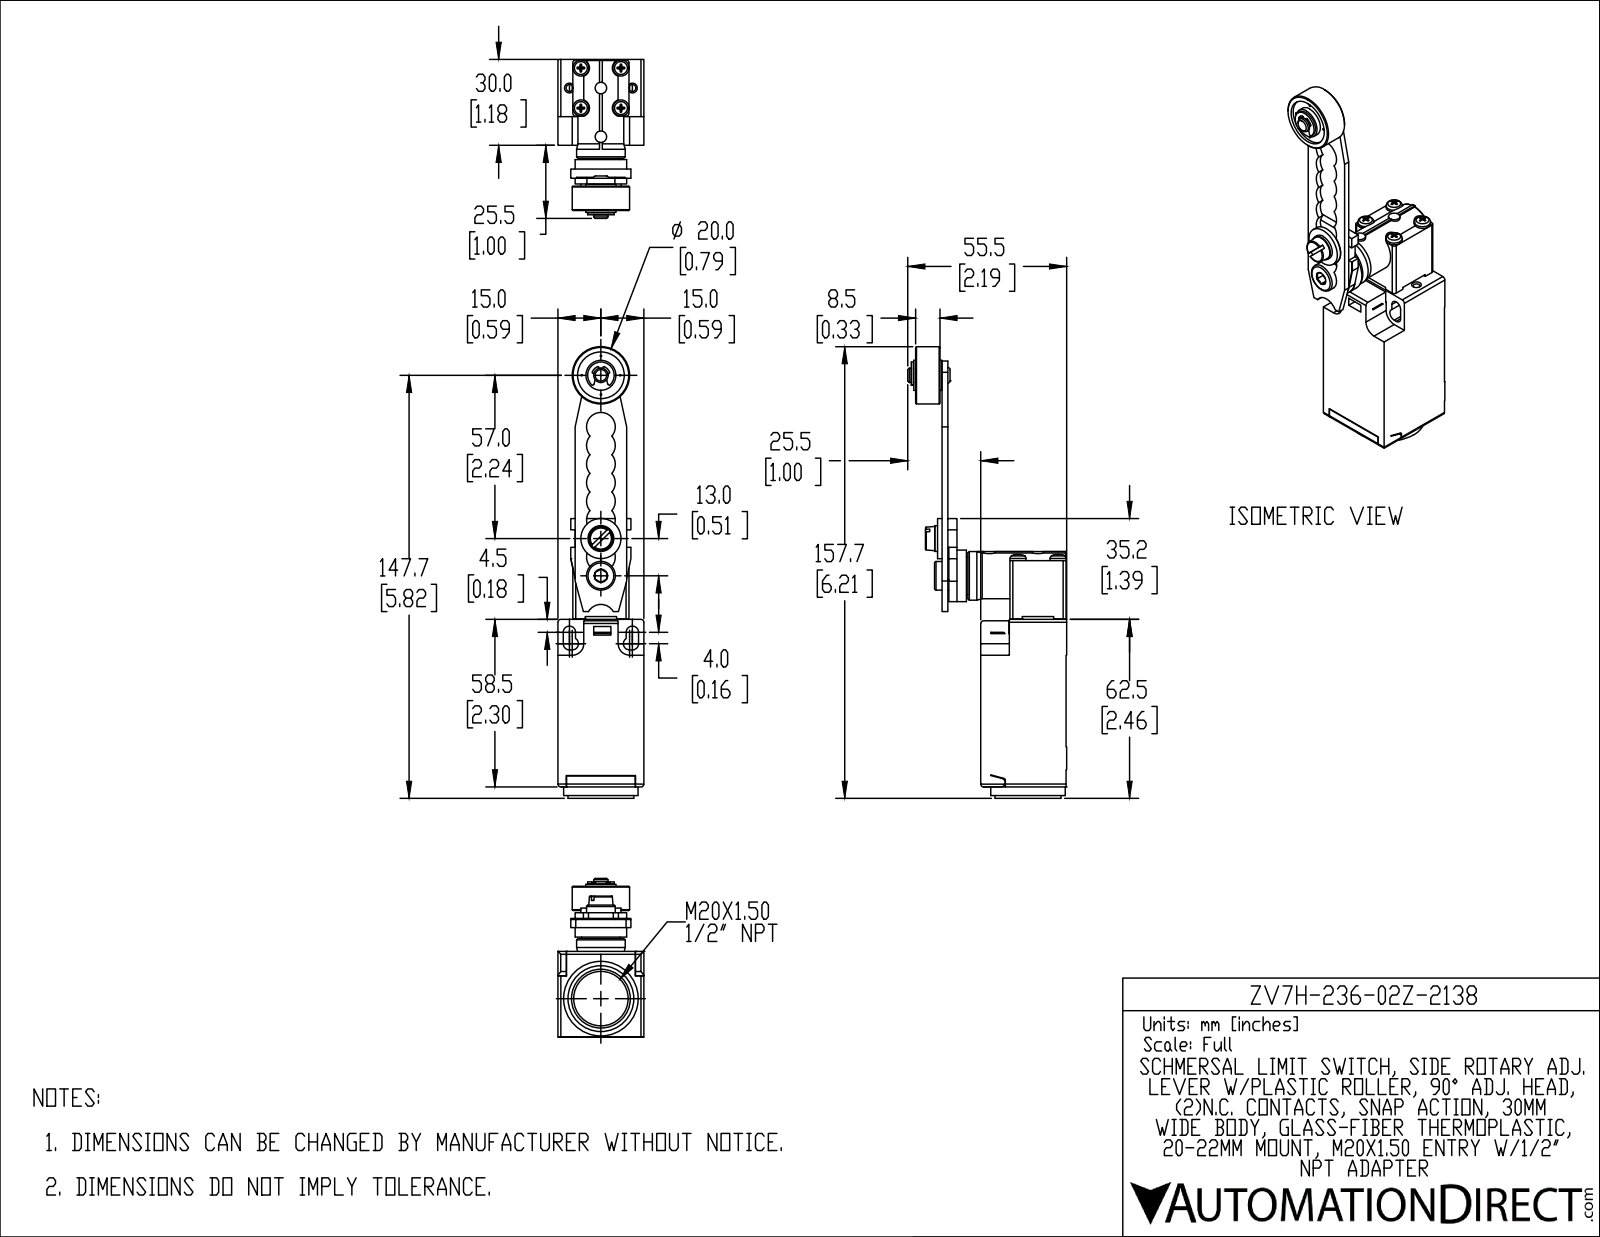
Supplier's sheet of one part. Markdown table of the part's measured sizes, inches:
| quantity | value |
| --- | --- |
| part name | ZV7H-236-02Z-2138 |
| STEP written by | SolidWorks 2019 (CONFIG_CONTROL_DESIGN) |
| units | inches |
| bodies | 6 solids, 542 faces (303 planar, 184 cylindrical, 55 other) |
| overall size | 6.209 × 2.185 × 1.181 |
| volume | 4.049 in³ |
| surface area | 32.22 in² |
| round holes (diameter × count) | 0.094 × 6, 0.02 × 4, 0.126 × 4, 0.512 × 1, 0.545 × 1, 0.642 × 1, 0.748 × 1 |
| round bosses / shafts (diameter × count) | 0.221 × 4, 0.213 × 4, 0.157 × 3, 1.024 × 1, 0.906 × 1, 0.787 × 1, 0.709 × 1, 0.669 × 1 |
| partial cylindrical surfaces (radius × count) | 0.197 × 11, 0.039 × 10, 0.085 × 6, 0.059 × 5, 0.012 × 4, 0.118 × 4, 0.02 × 2, 0.157 × 2 |
| main face-to-face distances | 1.181, 1.173, 0.205, 0.079, 0.531, 1.705, 0.453, 1.626, 0.976, 0.236 |
| hole center spacings | 0.266, 0.317, 0.376, 0.39, 0.551, 0.76, 0.308, 0.433 |
